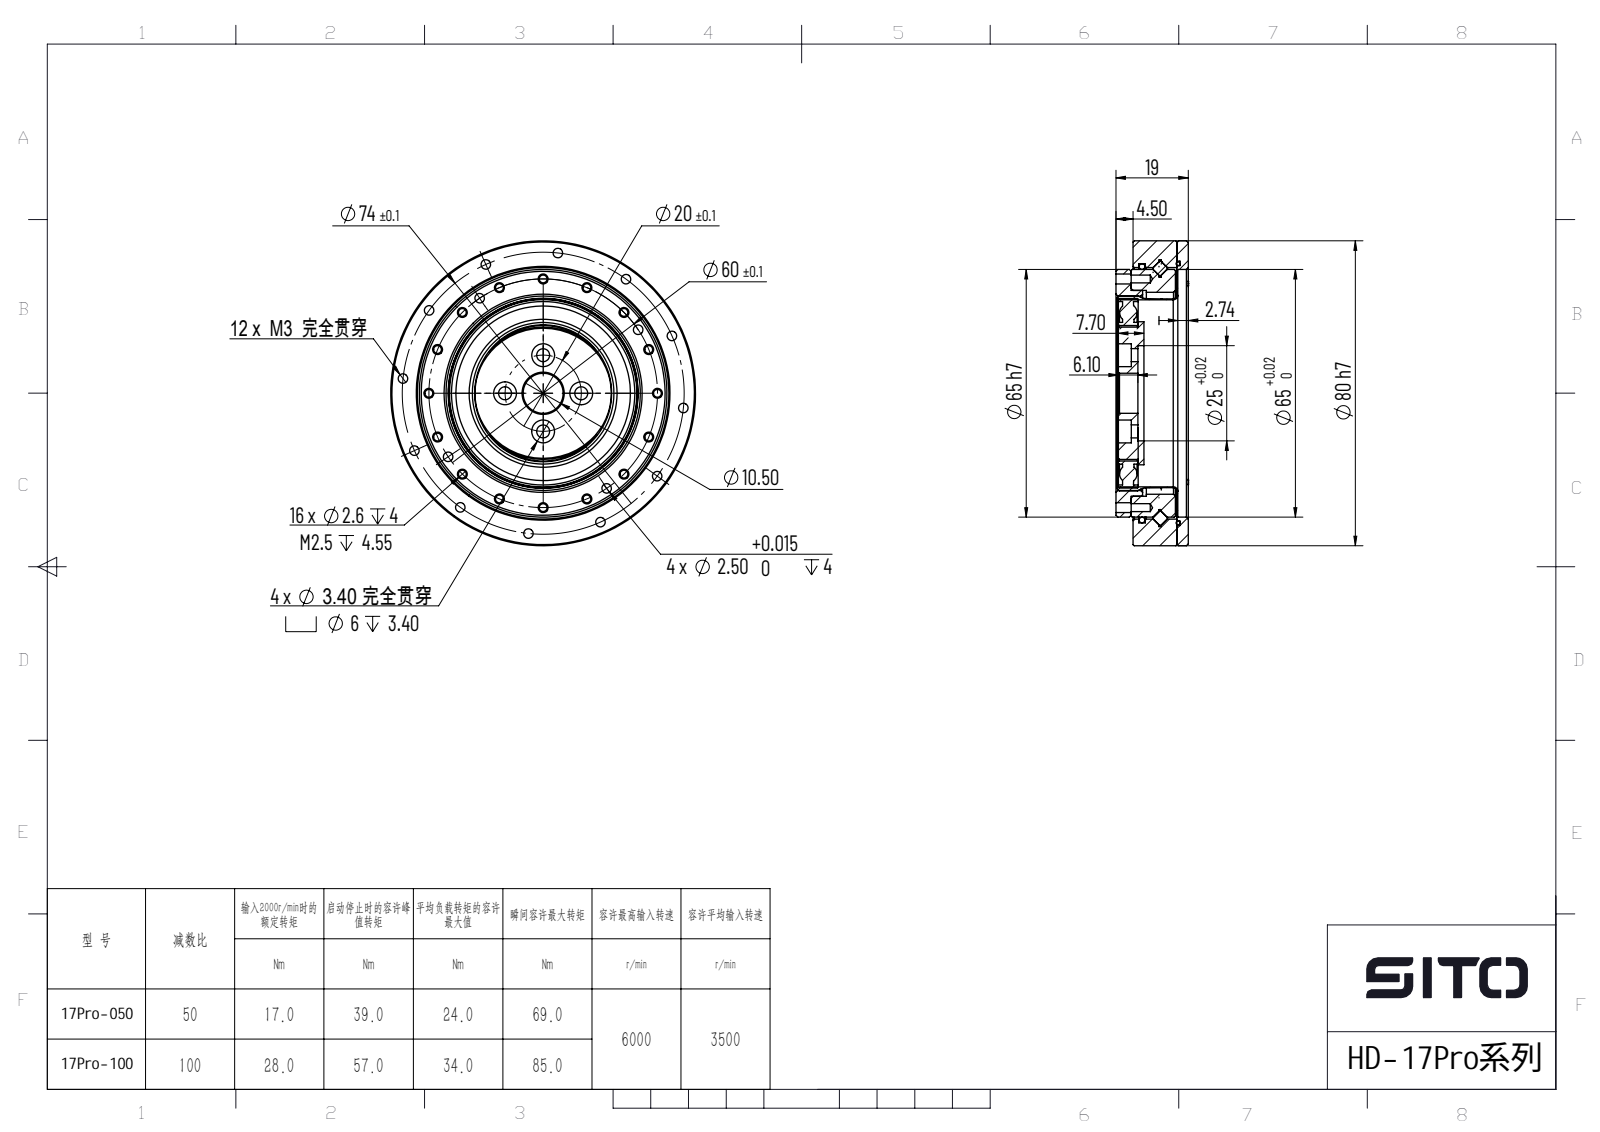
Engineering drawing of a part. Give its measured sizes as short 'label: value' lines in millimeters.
name: HD-17Pro-xxx; HD-17Pro_006; HD-17Pro_003; HD-17Pro???? <1> (+6 more)
written by: ONSHAPE BY PTC INC, 1.202 (AP242_MANAGED_MODEL_BASED_3D_ENGINEERING_MIM_LF)
unit: mm
bodies: 82 solids, 726 faces (287 planar, 198 cylindrical, 241 other)
size: 80 × 80 × 19.07
volume: 51 866 mm³; area: 48 615 mm²
holes: 16× ⌀2.05, 16× ⌀2.5, 16× ⌀2.6, 12× ⌀3.5, 5× ⌀1.6, 5× ⌀2.2, 4× ⌀3.4, 4× ⌀4.2, 4× ⌀6, 1× ⌀4.5, 1× ⌀10.5, 1× ⌀25
bosses: 68× ⌀3, 5× ⌀2, 4× ⌀4, 4× ⌀1.73, 1× ⌀80, 1× ⌀67, 1× ⌀65, 1× ⌀61
face distances: 12, 3.85, 3, 11.5, 0.5, 14.5, 15, 2.74, 11.76, 12.26
hole spacings: 37, 30, 52.32, 71.48, 49.89, 58.85, 22.96, 9.66
